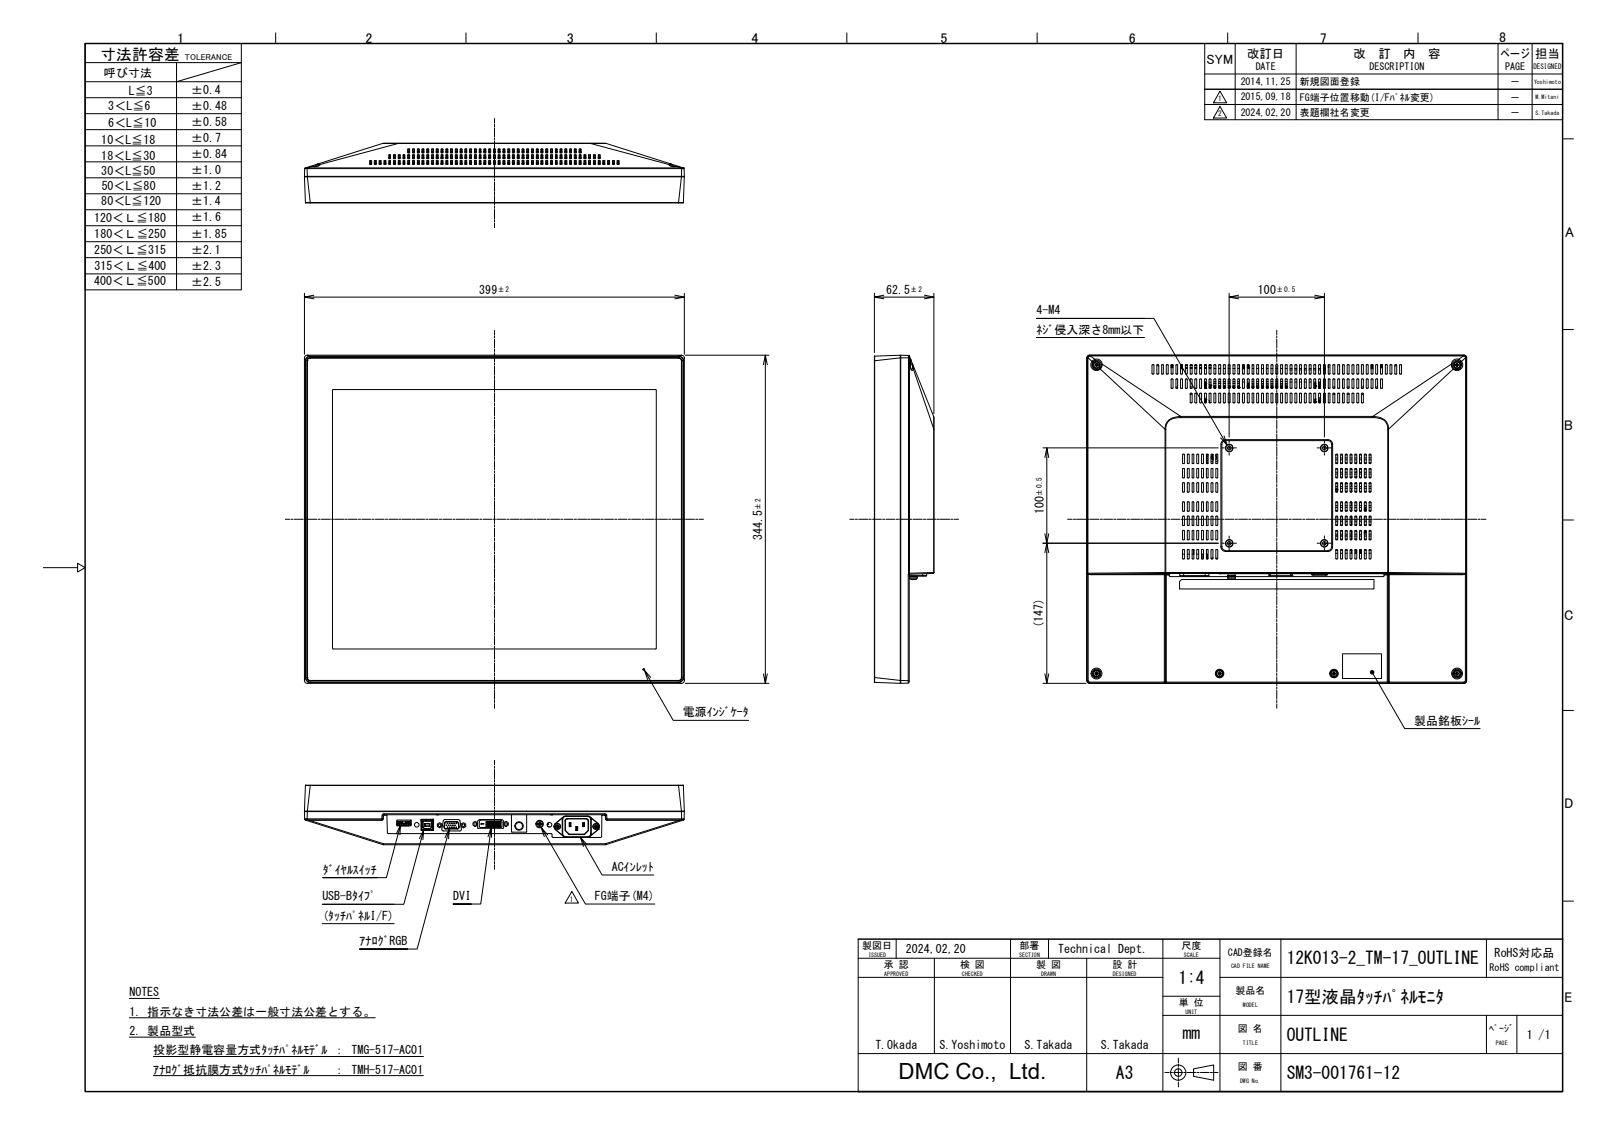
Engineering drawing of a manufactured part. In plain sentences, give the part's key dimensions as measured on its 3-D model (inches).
The part is named "HP_TMG(H)-517-AC01". Its 3-D file was written by "Autodesk Inventor 2017 (CONFIG_CONTROL_DESIGN)". It is 1 solid with 6732 faces: 3272 planar, 1446 cylindrical and 2014 other. Overall it measures 15.709 by 13.563 by 2.461 inches. Its volume is 64.99 cubic inches and its surface area 1 798 square inches. Round holes: 121 of diameter 0.138, 34 of diameter 0.315, 28 of diameter 0.097, 26 of diameter 0.157, 17 of diameter 0.039, 15 of diameter 0.118, 13 of diameter 0.126, 5 of diameter 0.189, 4 of diameter 0.079, 4 of diameter 0.354, 4 of diameter 0.394, 2 of diameter 0.102. Round bosses or shafts: 16 of diameter 0.242, 16 of diameter 0.118, 12 of diameter 0.142, 6 of diameter 0.281, 5 of diameter 0.157, 4 of diameter 0.244, 4 of diameter 0.165, 4 of diameter 0.161. Partial cylindrical surfaces (rounded edges, fillets, slot ends): 202 of radius 0.02, 126 of radius 0.039, 24 of radius 0.012, 18 of radius 0.051, 14 of radius 0.063, 13 of radius 0.004, 13 of radius 0.079, 10 of radius 0.118. The main face-to-face distances are 0.039, 0.118, 1.026, 1.066, 0.983, 1.022, 0.043, 1.024, 0.217, 0.984. The hole center spacings are 0.197, 0.09, 0.44, 0.394, 0.622, 0.278, 0.591, 0.156.
